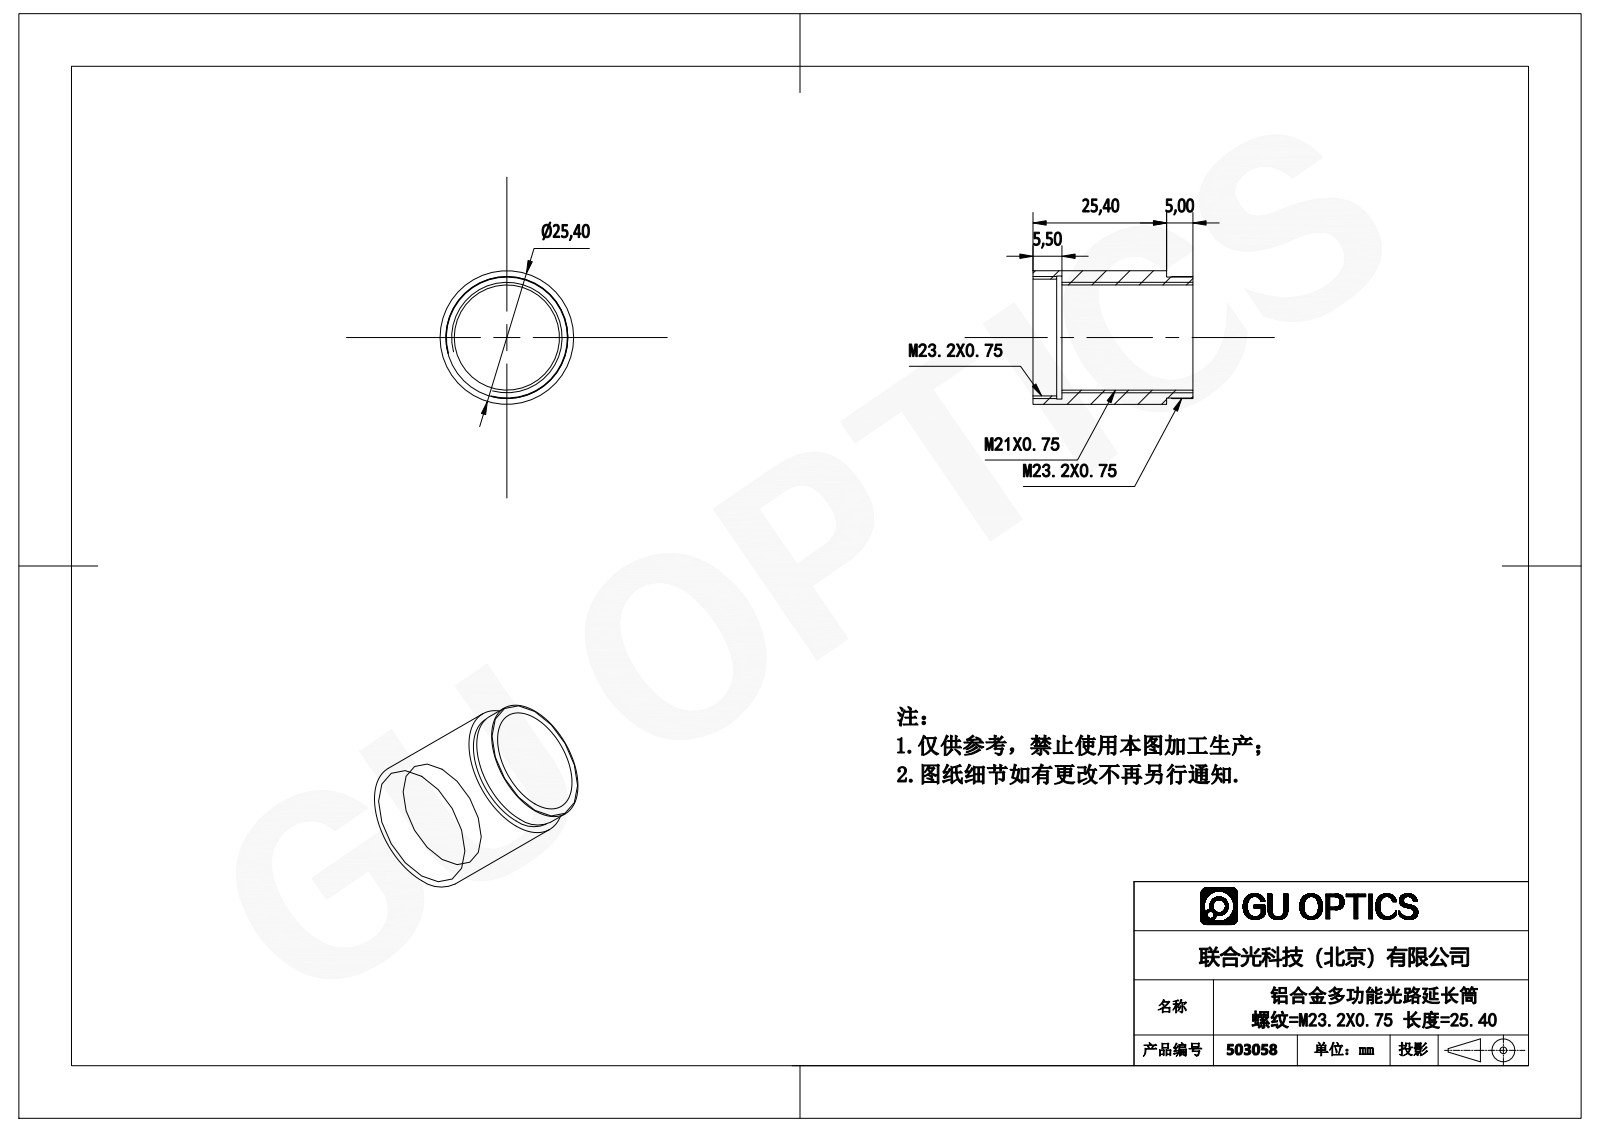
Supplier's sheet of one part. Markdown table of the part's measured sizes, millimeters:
| quantity | value |
| --- | --- |
| part name | 503058 |
| STEP written by | SolidWorks 2016 (AUTOMOTIVE_DESIGN) |
| units | millimeters |
| bodies | 1 solid, 18 faces (6 planar, 12 cylindrical, 0 other) |
| overall size | 30.4 × 25.4 × 25.4 |
| volume | 4 982 mm³ |
| surface area | 4 828 mm² |
| round holes (diameter × count) | 20 × 1, 22.2 × 1, 23.4 × 1 |
| round bosses / shafts (diameter × count) | 25.4 × 1, 23.2 × 1, 23 × 1 |
| main face-to-face distances | 5.5, 30.4, 24.9, 25.4, 19.9, 5, 1, 20.9, 4.5, 25.9 |
